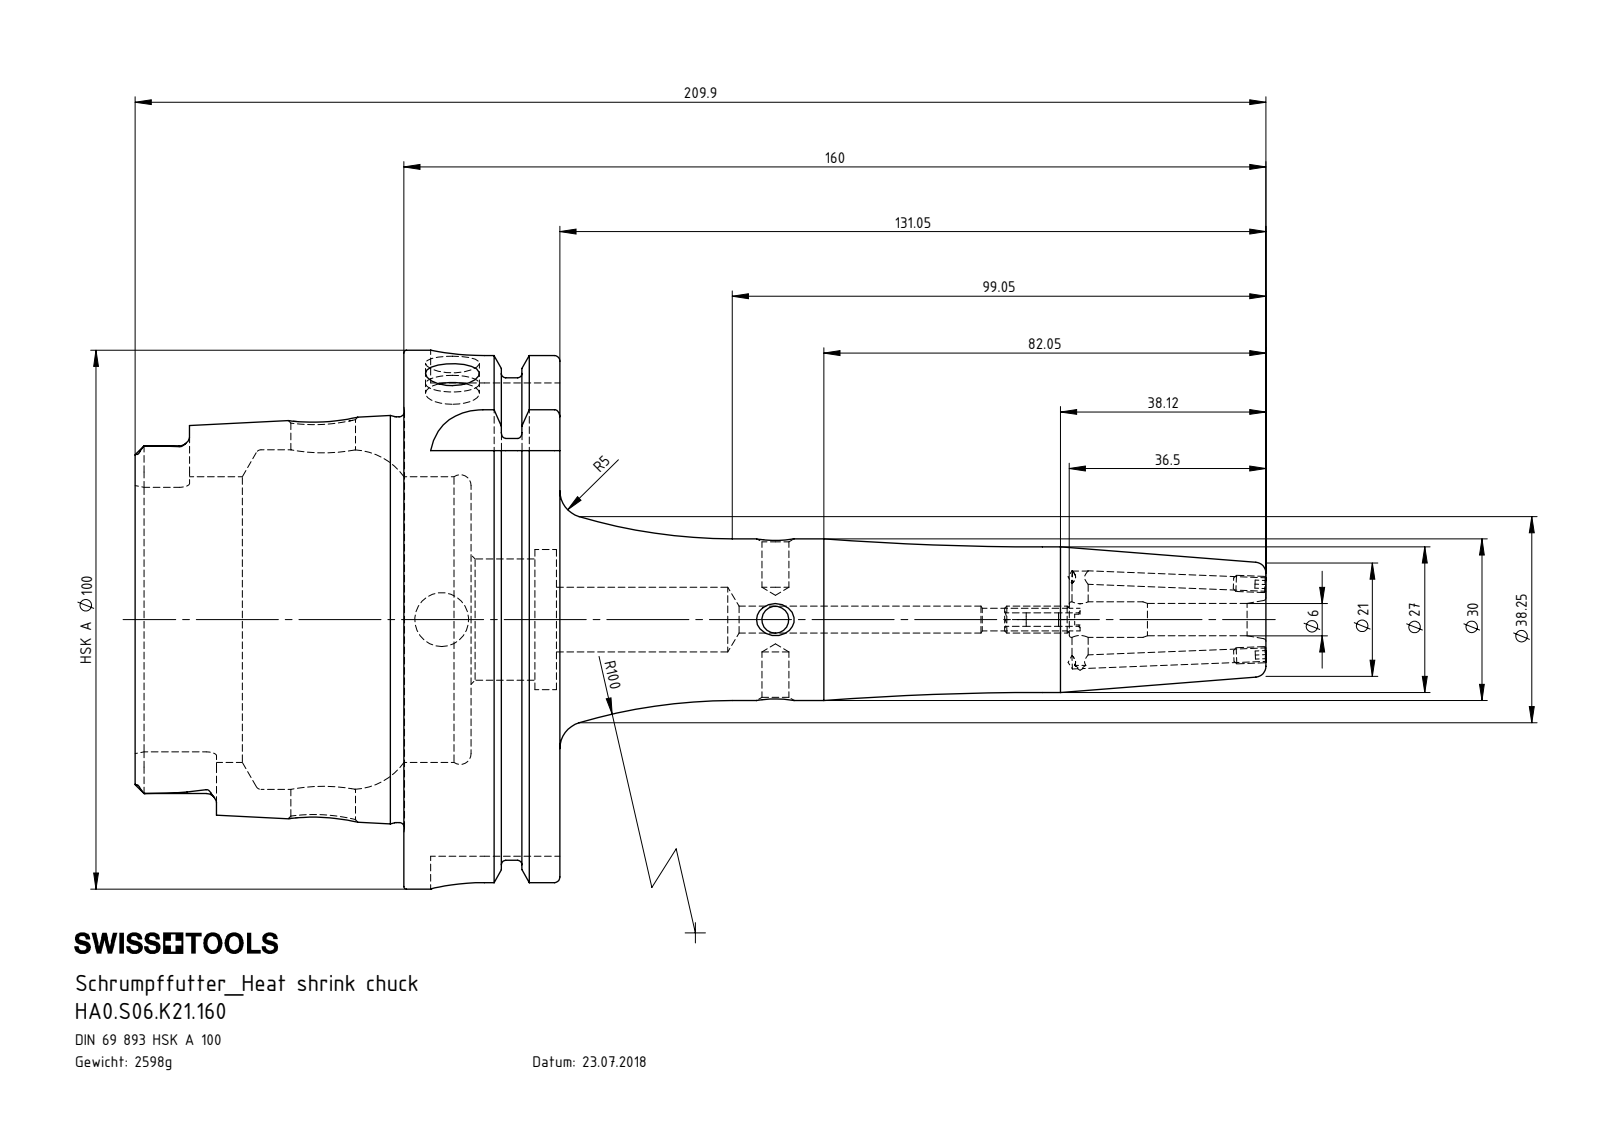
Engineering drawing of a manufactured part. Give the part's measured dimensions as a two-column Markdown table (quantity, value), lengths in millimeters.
| quantity | value |
| --- | --- |
| part name | HA0-S06.K21.160_C_Fertigbearbeitung; ERU-AN1.K01.014_A; ERU-CJ2.001.006; HA0.S06.K21.160 |
| STEP written by | SolidWorks 2017 (CONFIG_CONTROL_DESIGN) |
| units | millimeters |
| bodies | 4 solids, 312 faces (95 planar, 93 cylindrical, 124 other) |
| overall size | 209.98 × 100 × 100 |
| volume | 330 958 mm³ |
| surface area | 65 014 mm² |
| round holes (diameter × count) | 2.5 × 3, 5 × 3, 10 × 3, 12 × 2, 3 × 1, 4.2 × 1, 6 × 1, 6.6 × 1, 22.5 × 1, 26 × 1, 53 × 1, 63 × 1 |
| round bosses / shafts (diameter × count) | 3 × 2, 100 × 1, 91.95 × 1, 75.26 × 1, 30 × 1, 27 × 1 |
| partial cylindrical surfaces (radius × count) | 1.9 × 6, 4.88 × 4, 10 × 4 |
| main face-to-face distances | 28.95, 12.45, 16.5, 49.9, 62.35, 78.85, 87.8, 78.2, 28.3, 15.85 |
| hole center spacings | 56.55, 61.95, 83.95, 140.5 |
